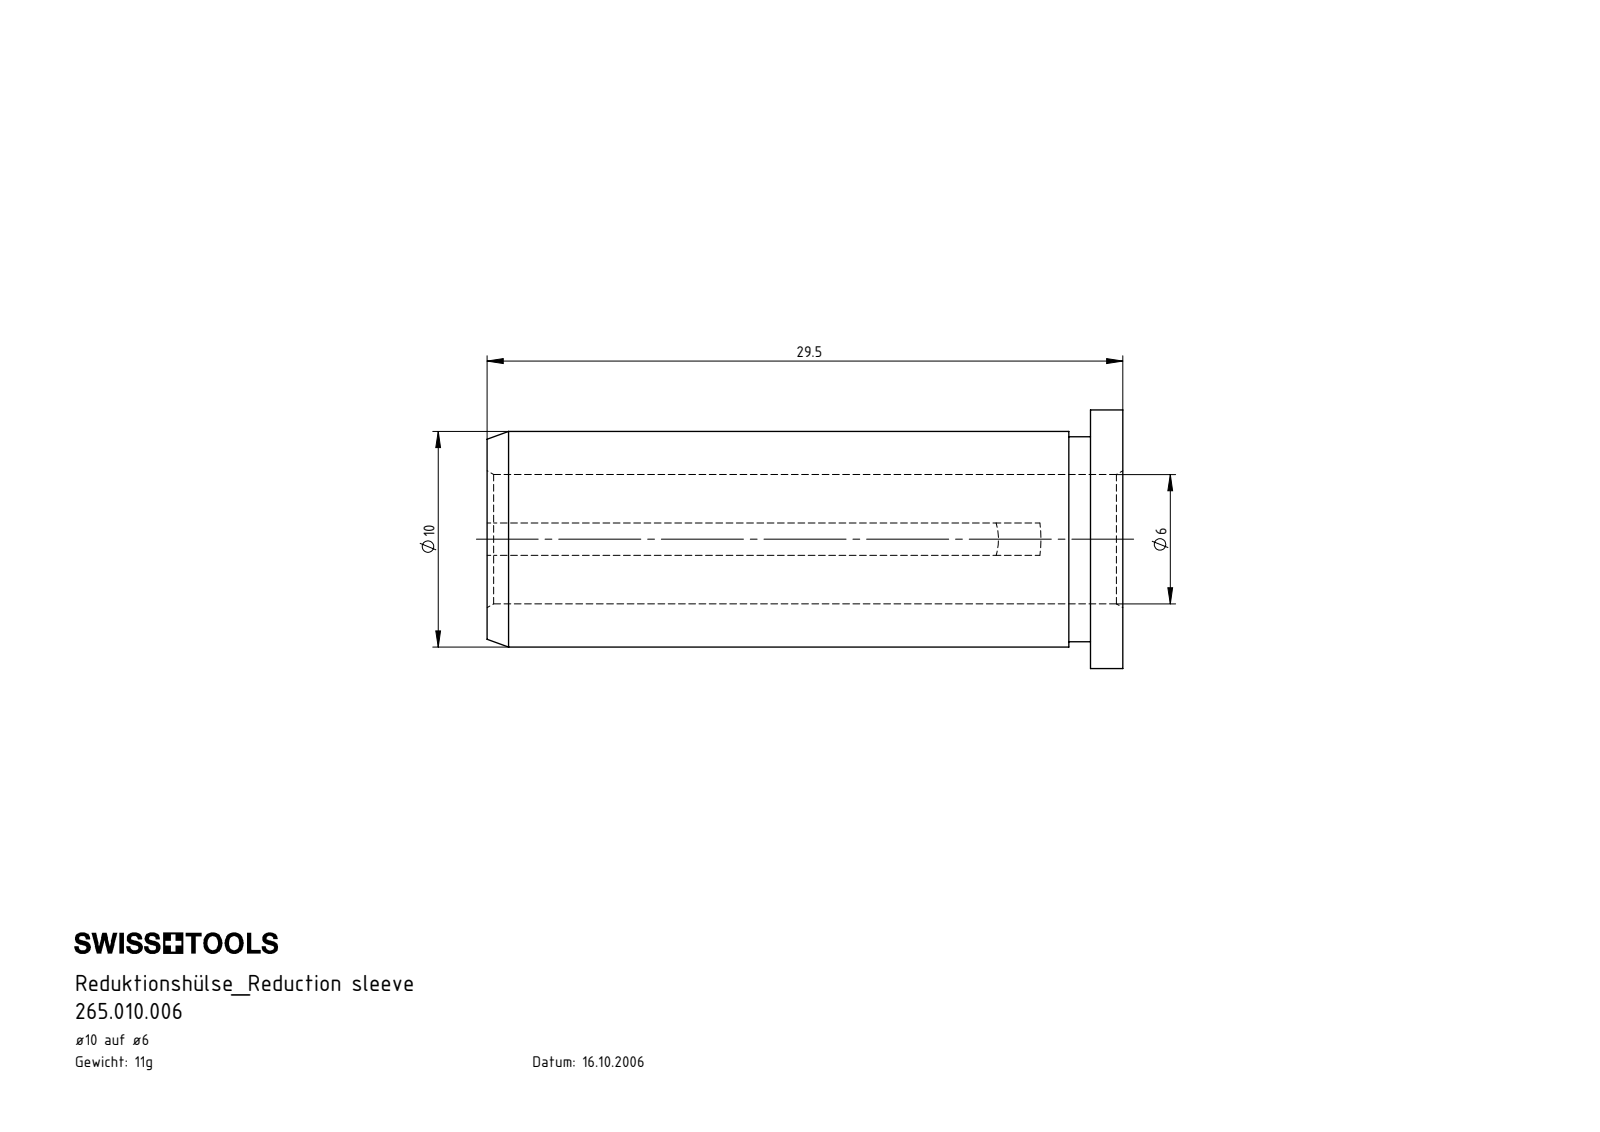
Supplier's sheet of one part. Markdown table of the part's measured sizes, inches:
| quantity | value |
| --- | --- |
| part name | U06-U10.001.030_A |
| STEP written by | SolidWorks 2012 (CONFIG_CONTROL_DESIGN) |
| units | inches |
| bodies | 1 solid, 23 faces (6 planar, 9 cylindrical, 8 other) |
| overall size | 1.161 × 0.472 × 0.472 |
| volume | 0.088 in³ |
| surface area | 2.616 in² |
| round holes (diameter × count) | 0.236 × 1 |
| round bosses / shafts (diameter × count) | 0.472 × 1, 0.394 × 1, 0.374 × 1 |
| partial cylindrical surfaces (radius × count) | 0.787 × 1 |
| main face-to-face distances | 0.059, 1.102, 1.161, 1.063, 0.039, 0.098 |
